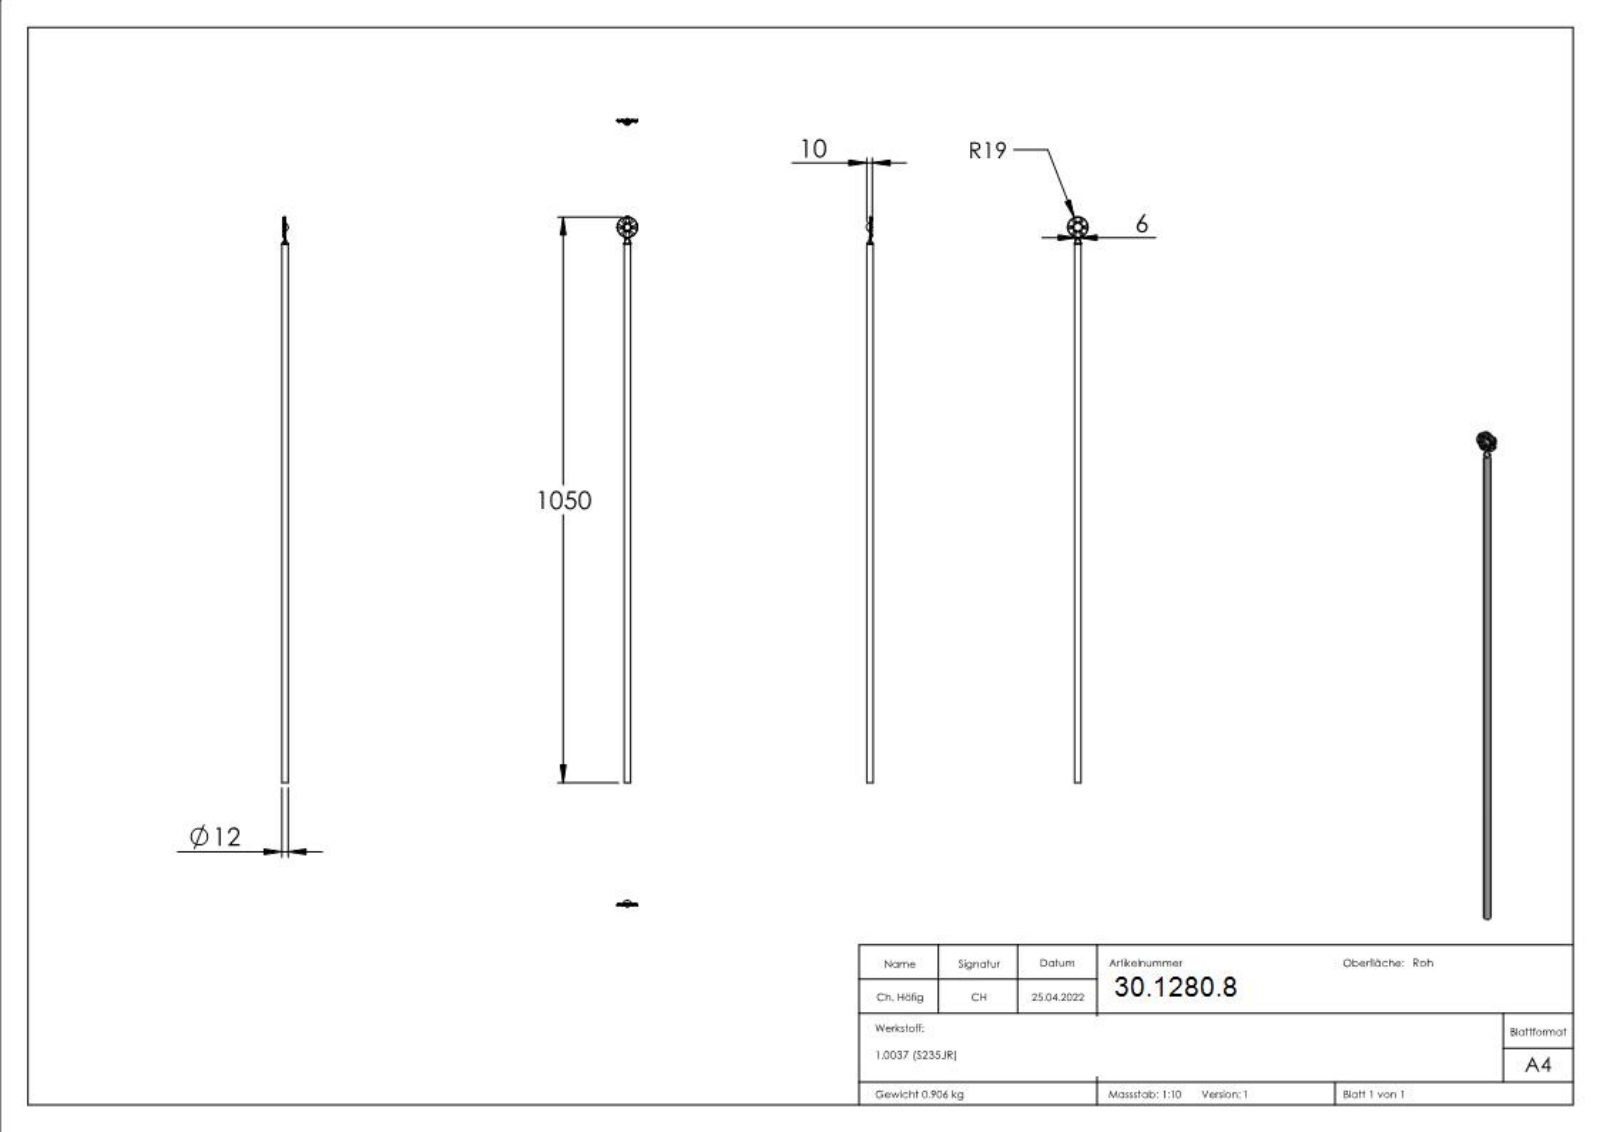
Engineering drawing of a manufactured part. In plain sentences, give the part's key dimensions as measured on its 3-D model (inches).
The part is named "1692". Its 3-D file was written by "SolidWorks 2018 (CONFIG_CONTROL_DESIGN)". It is 1 solid with 377 faces: 119 planar, 6 cylindrical and 252 other. Overall it measures 41.339 by 1.496 by 0.472 inches. Its volume is 7.086 cubic inches and its surface area 63.44 square inches. Round bosses or shafts: 1 of diameter 1.496, 1 of diameter 0.472. Partial cylindrical surfaces (rounded edges, fillets, slot ends): 4 of radius 0.008. The main face-to-face distances are 0.02, 0.087, 0.018, 0.022, 0.109, 0.161, 0.027, 0.013, 0.064, 0.057.
